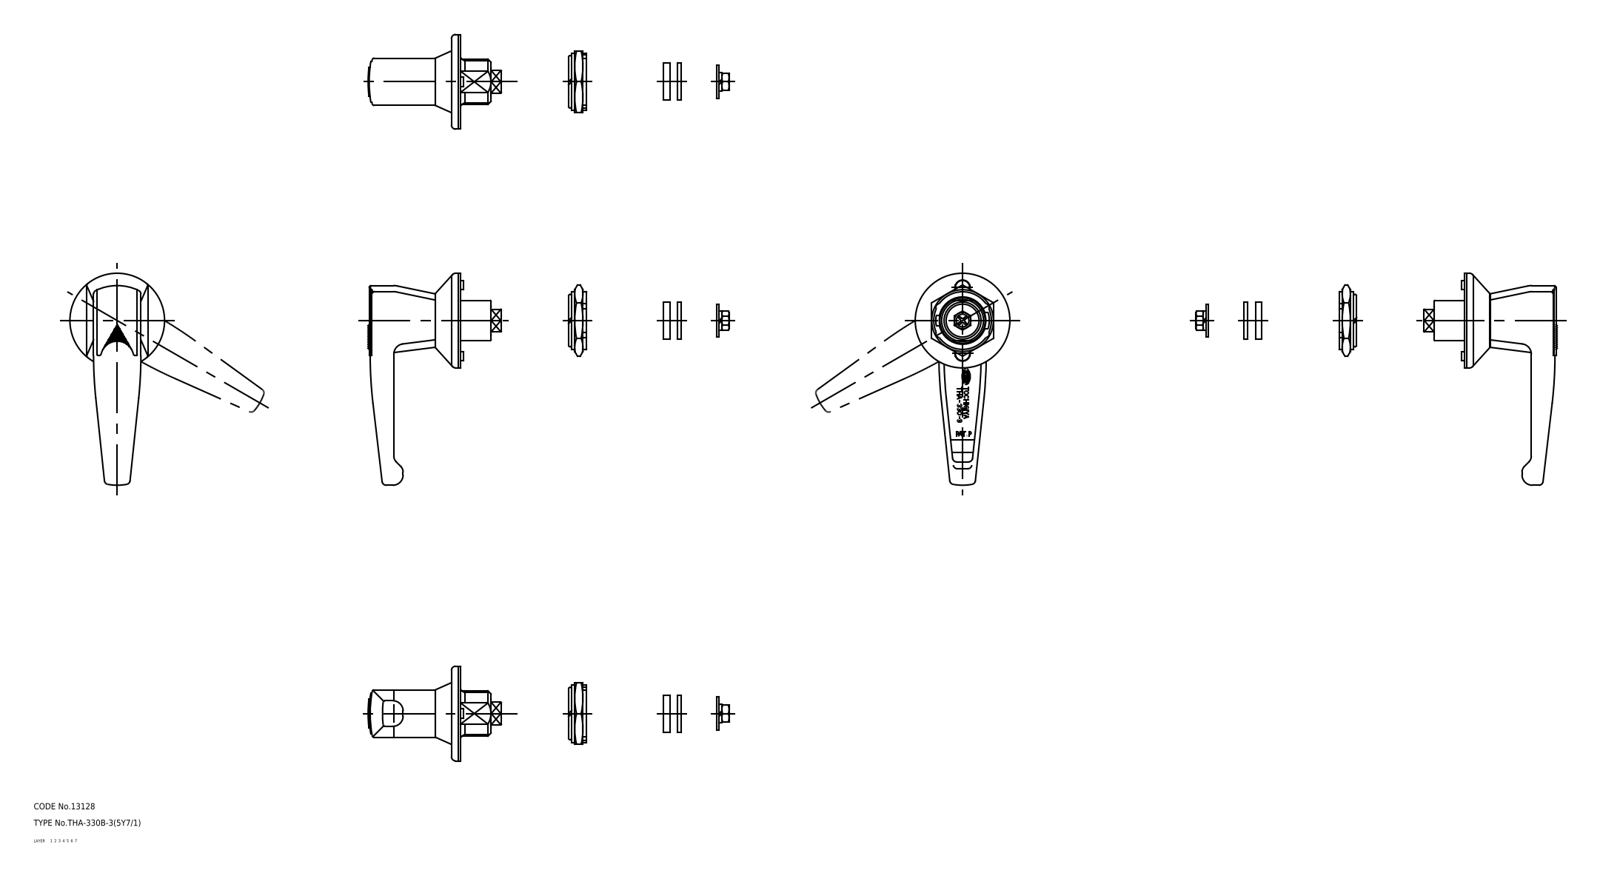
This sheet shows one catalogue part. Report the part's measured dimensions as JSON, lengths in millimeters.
{"part_name": "washer_D; washer_C; washer_B; washer_A (+6 more)", "step_written_by": "CADfix (AUTOMOTIVE_DESIGN)", "units": "millimeters", "bodies": {"solids": 9, "faces": 329, "planar": 0, "cylindrical": 0, "other": 329}, "overall_size": [103, 70.8, 46], "volume_mm3": 50878, "surface_area_mm2": 23446}
